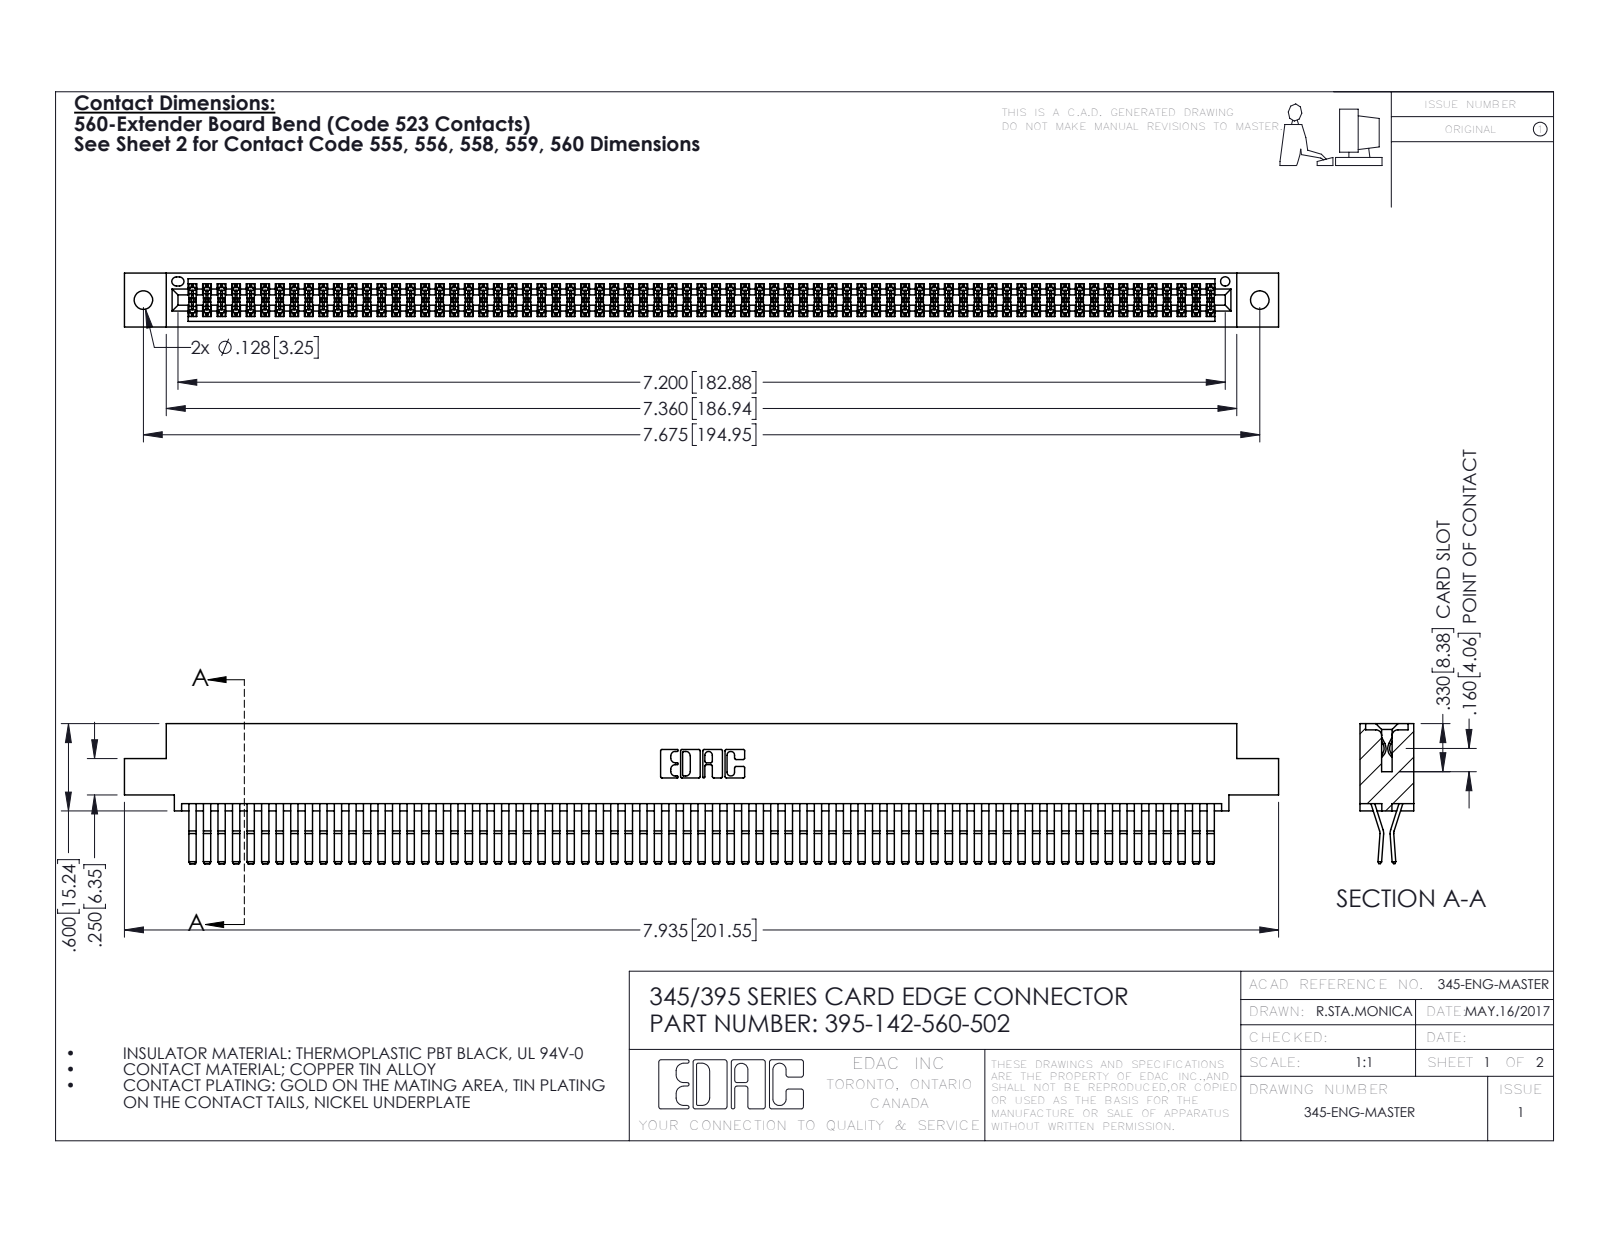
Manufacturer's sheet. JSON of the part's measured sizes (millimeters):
{"part_name": "395-142-560-502; 345 Part_0.110 Offset - 0.128 Dia; 345-292-001_560 Tail", "step_written_by": "SolidWorks 2016 (CONFIG_CONTROL_DESIGN)", "units": "millimeters", "bodies": {"solids": 143, "faces": 7514, "planar": 4770, "cylindrical": 2744, "other": 0}, "overall_size": [201.5, 24.4, 9.4], "volume_mm3": 20660, "surface_area_mm2": 33330, "round_holes": [[3.3, 2], [1.6, 1]], "partial_cylinders_radius": [[0.2, 213], [0.3, 22], [0.2, 6], [0.8, 6], [0.7, 3], [0.3, 2], [0.4, 2], [0.5, 2]], "face_to_face_distances": [0.6, 7.6, 1.8, 9.4, 5.1, 2.5, 6.9, 5.7, 4.4, 3.8], "hole_center_spacings": [6.9, 189, 194.9]}
